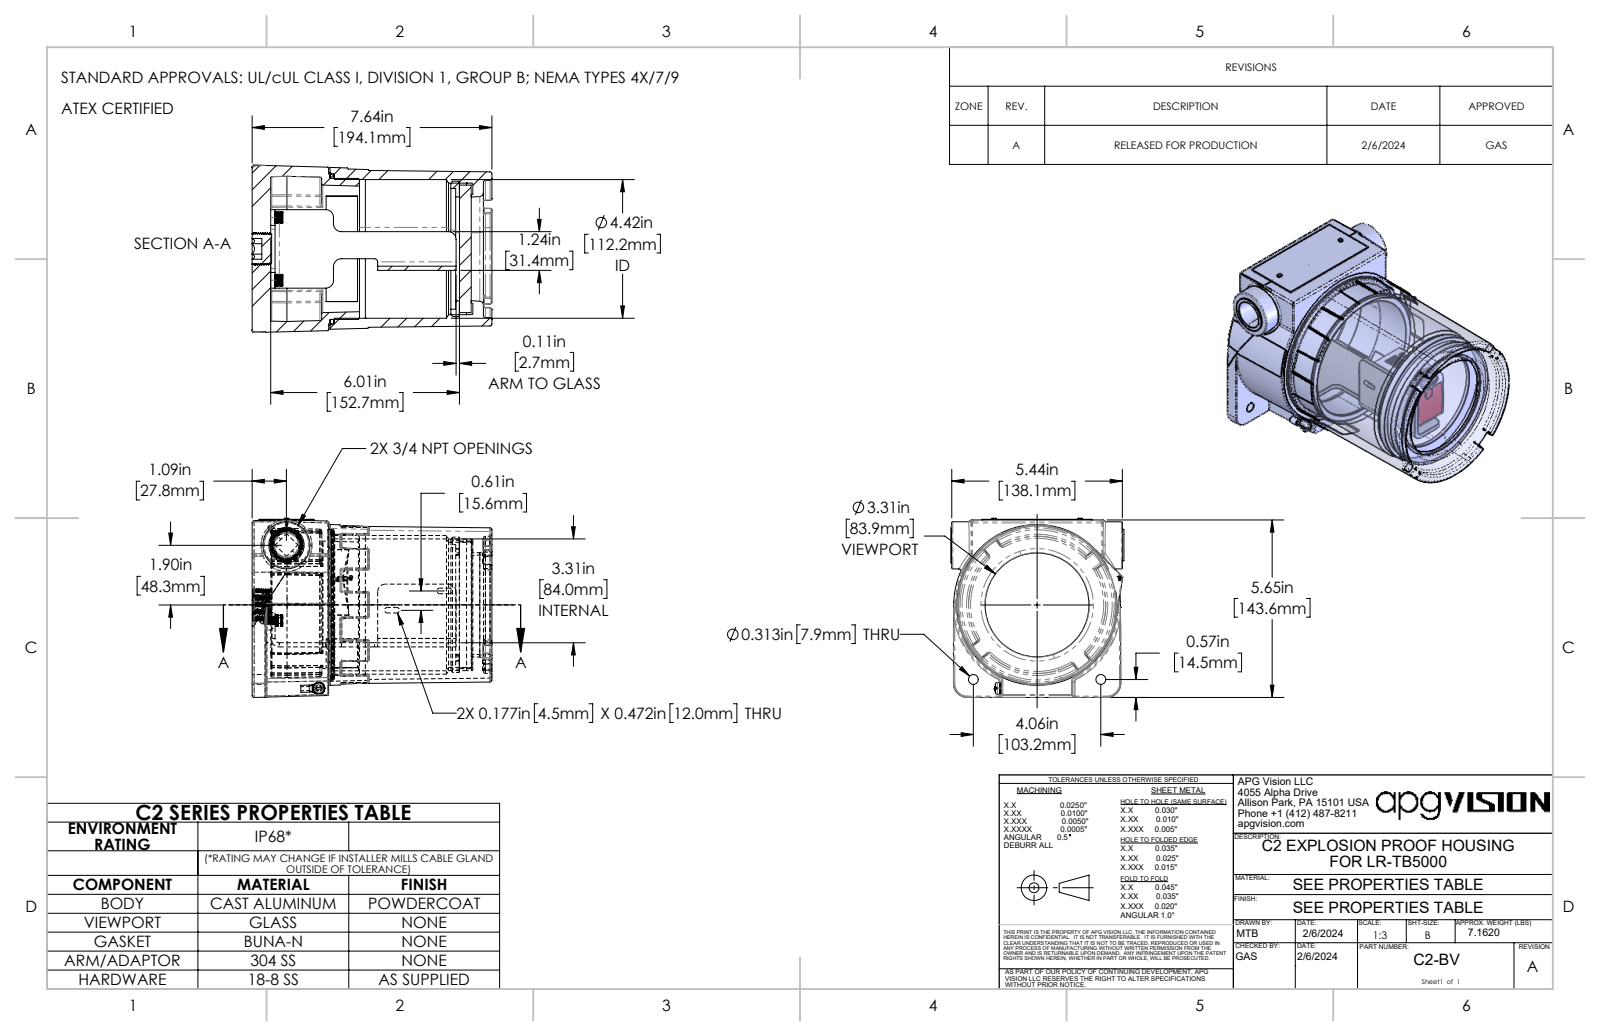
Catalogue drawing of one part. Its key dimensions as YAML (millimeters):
part_name: "92196A535_92196A535; 4638K515_4638K515; 201944; C2-BV (+2 more)"
step_written_by: "SolidWorks 2022 (CONFIG_CONTROL_DESIGN)"
units: millimeters
bodies: {solids: 21, faces: 1788, planar: 549, cylindrical: 361, other: 878}
overall_size: [194.1, 145, 140.2]
volume: 1164000
surface_area: 317300
round_holes:
  - {diameter: 1.7, count: 2}
  - {diameter: 2.4, count: 2}
  - {diameter: 3.7, count: 2}
  - {diameter: 4.2, count: 2}
  - {diameter: 4.8, count: 2}
  - {diameter: 5.1, count: 2}
  - {diameter: 6.8, count: 2}
  - {diameter: 8, count: 2}
  - {diameter: 10.2, count: 2}
  - {diameter: 2.7, count: 1}
  - {diameter: 3.3, count: 1}
  - {diameter: 5, count: 1}
round_bosses_or_shafts:
  - {diameter: 6.4, count: 2}
  - {diameter: 4.8, count: 2}
  - {diameter: 4.7, count: 2}
  - {diameter: 1.9, count: 2}
  - {diameter: 121.2, count: 1}
  - {diameter: 114.1, count: 1}
  - {diameter: 109.5, count: 1}
  - {diameter: 103.2, count: 1}
partial_cylinders:
  - {radius: 0.8, count: 19}
  - {radius: 0.5, count: 16}
  - {radius: 0.8, count: 11}
  - {radius: 0.3, count: 10}
  - {radius: 6.4, count: 9}
  - {radius: 0.2, count: 8}
  - {radius: 2, count: 7}
  - {radius: 1.6, count: 5}
face_to_face_distances: [15.1, 177.3, 162.3, 3.4, 167.8, 152.7, 9.5, 0.5, 103.3, 99.9]
hole_center_spacings: [28.4, 18, 40.2, 45.2, 52.3, 54.4, 73.2, 79.4]
